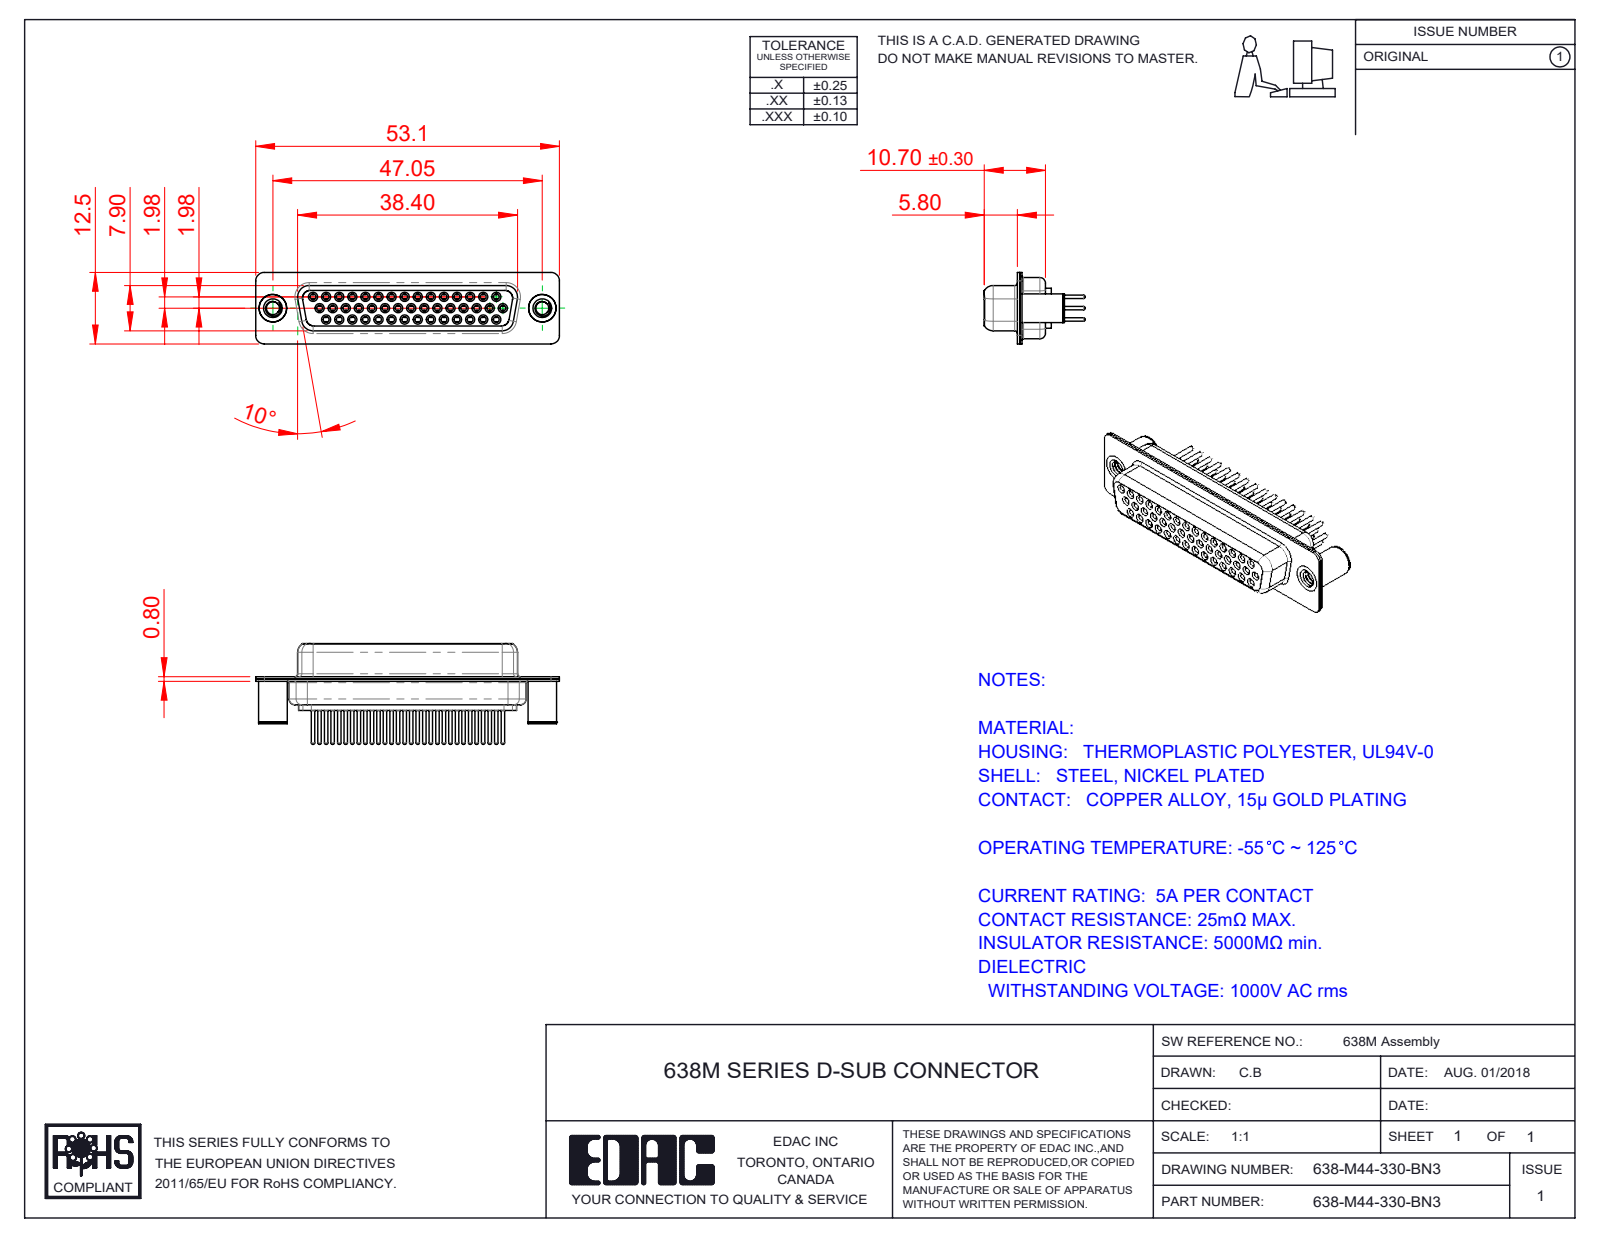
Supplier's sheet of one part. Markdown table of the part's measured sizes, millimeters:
| quantity | value |
| --- | --- |
| part name | 638M 4-40 Threaded Board Spacer; 638M Contact Row 2_30; 638M Contact Row 3_30; 638M Contact Row 1_30 (+4 more) |
| STEP written by | SolidWorks 2020 (CONFIG_CONTROL_DESIGN) |
| units | millimeters |
| bodies | 49 solids, 2733 faces (727 planar, 997 cylindrical, 1009 other) |
| overall size | 53.05 × 17.6 × 12.5 |
| volume | 3 659 mm³ |
| surface area | 12 277 mm² |
| round holes (diameter × count) | 1 × 44, 1.1 × 44, 1.7 × 44, 1.8 × 44, 2 × 44, 2.26 × 2, 3.26 × 2, 4 × 2, 4.8 × 2 |
| round bosses / shafts (diameter × count) | 2.2 × 44, 1.6 × 44, 1.5 × 44, 0.6 × 44, 5 × 2, 4.9 × 2 |
| partial cylindrical surfaces (radius × count) | 1.5 × 16, 2 × 12, 1.35 × 9, 1.6 × 8, 0.25 × 4, 0.5 × 4, 0.6 × 4, 0.65 × 4 |
| main face-to-face distances | 0.4, 1.4, 0.45, 8.45, 8.9, 1.8, 1, 6.2, 7.05, 1.85 |
| hole center spacings | 2.28, 2.29, 3.96, 4.57, 8.24, 6.86, 11.43, 14.99 |
